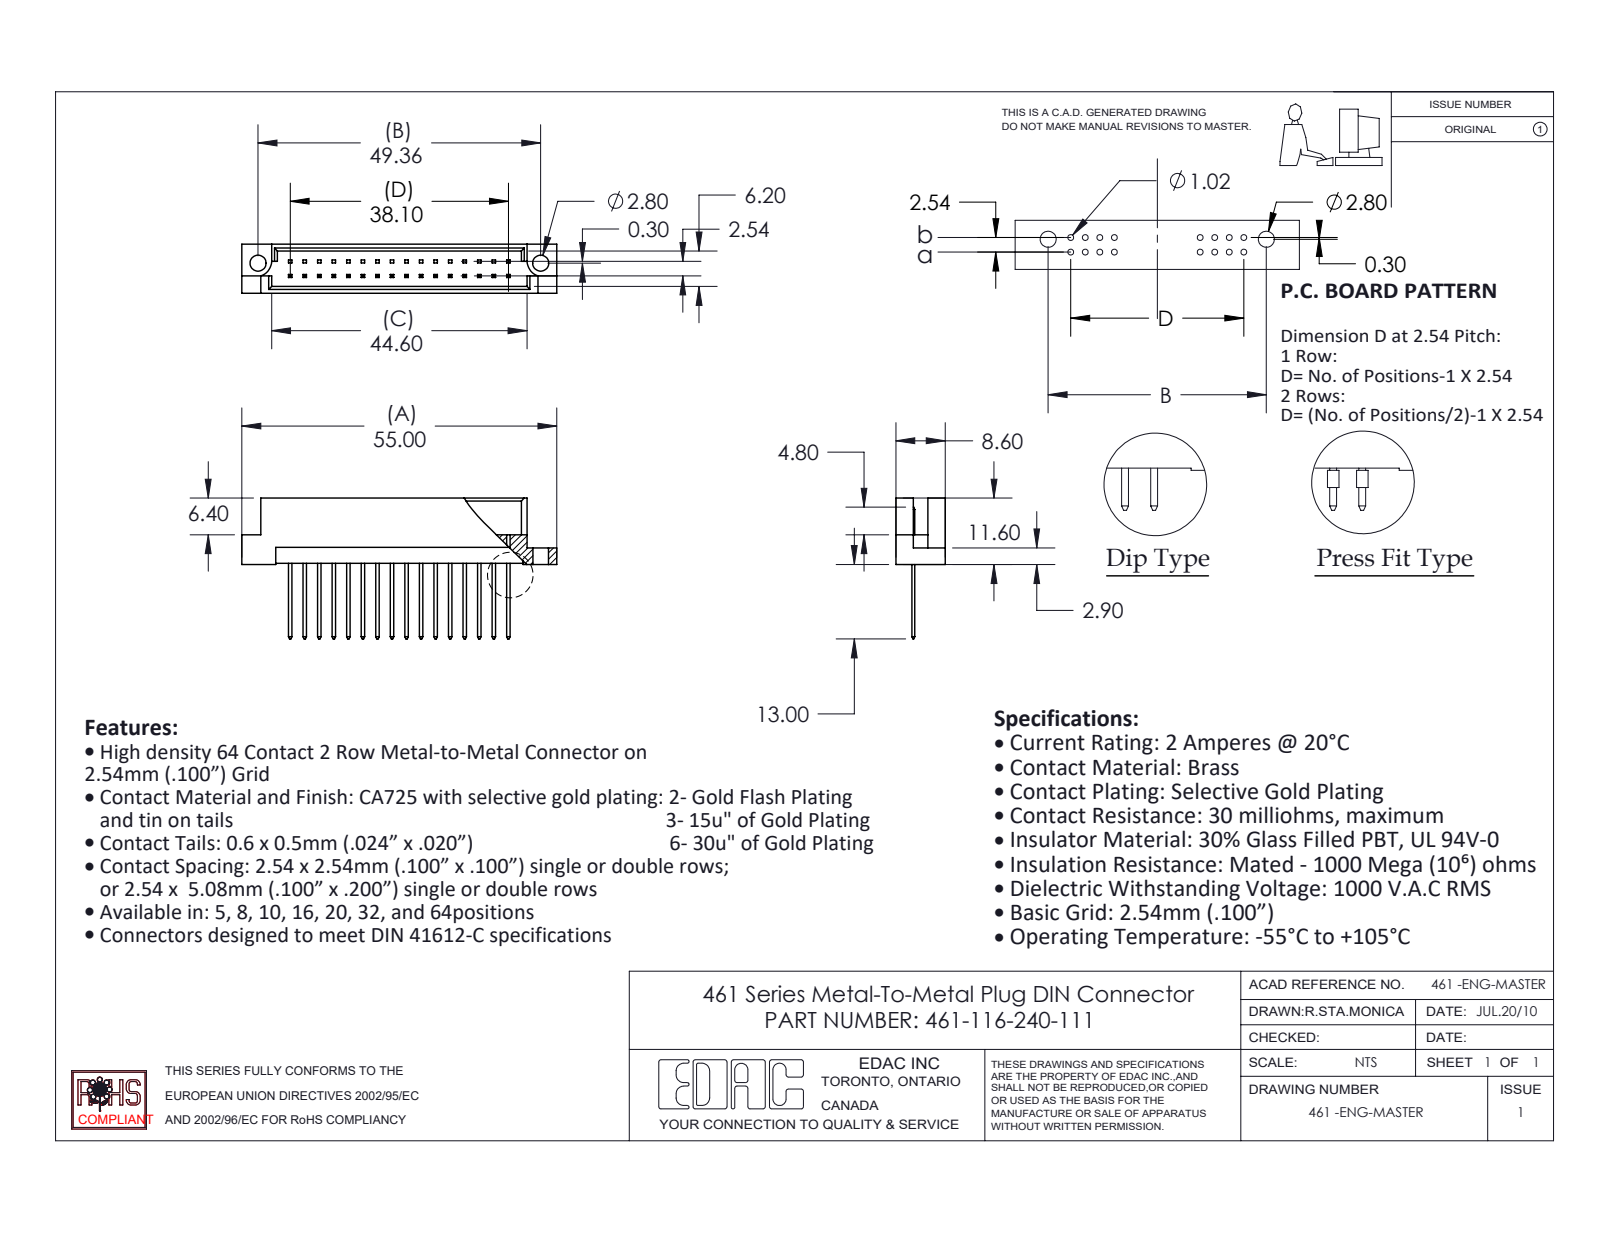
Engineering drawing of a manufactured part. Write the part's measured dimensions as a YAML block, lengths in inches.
part_name: "461-290_40; 461 Part_32; 461-116-240-111"
step_written_by: "SolidWorks 2020 (CONFIG_CONTROL_DESIGN)"
units: inches
bodies: {solids: 17, faces: 400, planar: 394, cylindrical: 6, other: 0}
overall_size: [2.165, 0.969, 0.339]
volume: 0.169
surface_area: 6.279
round_holes:
  - {diameter: 0.11, count: 2}
partial_cylinders:
  - {radius: 0.11, count: 2}
face_to_face_distances: [0.047, 0.291, 0.339, 0.244, 0.1, 0.109, 0.229, 0.062, 0.182, 0.129]
hole_center_spacings: [1.943]
